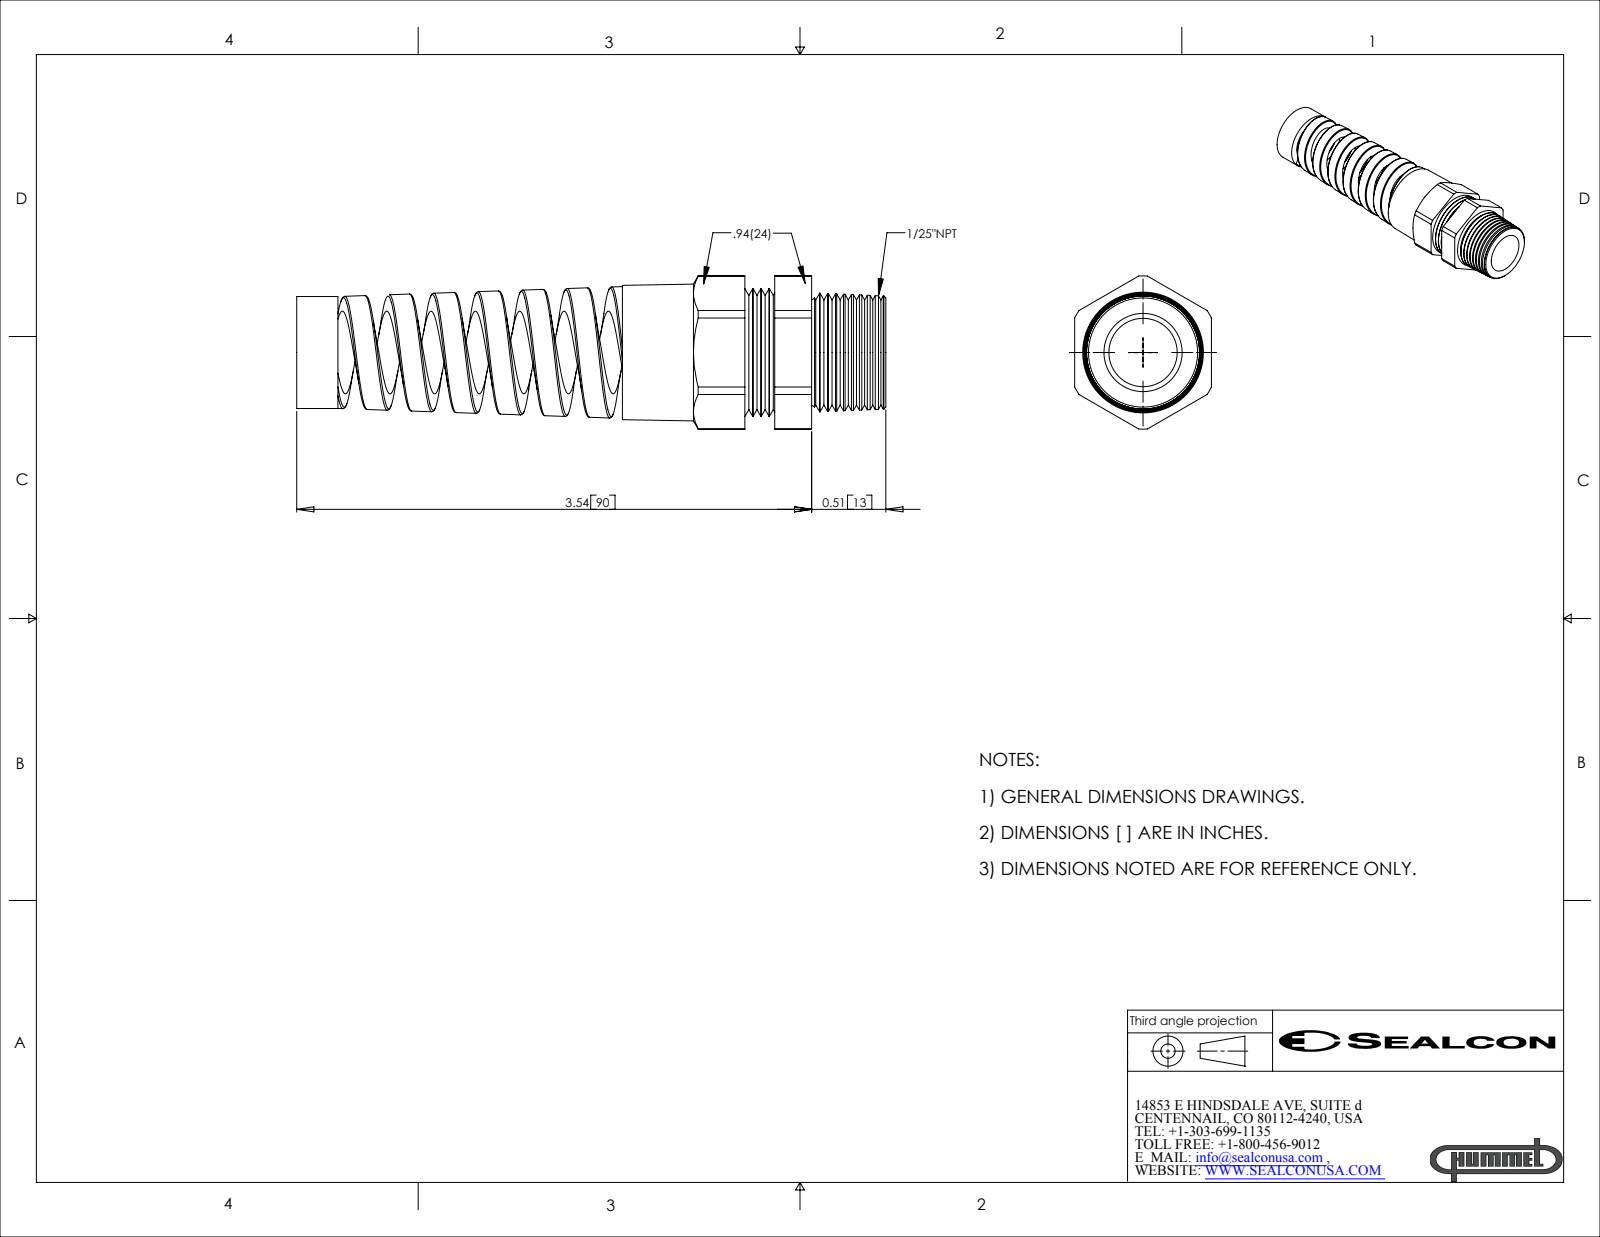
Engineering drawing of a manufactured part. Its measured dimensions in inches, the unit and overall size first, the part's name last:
Units: inches
Overall size (bounding box): 4.05 × 1.053 × 0.94
Round holes (diameter × count): ⌀0.47 ×1, ⌀0.569 ×1
Round bosses / shafts (diameter × count): ⌀0.88 ×1, ⌀0.769 ×1
Partial cylindrical surfaces — rounded edges, fillets, slot ends (radius × count): R0.526 ×1
Main face-to-face distances: 0.94, 1.301, 1.811, 0.51, 2.239, 3.54, 4.05, 3.287, 1.048, 0.254
Volume: 1.176 in³ · Surface area: 20.68 in²
Bodies: 1 solid, 164 faces (19 planar, 39 cylindrical, 106 other)
Part name (STEP PRODUCT): CF13NA-GY
STEP written by: SolidWorks 2007 (CONFIG_CONTROL_DESIGN)
